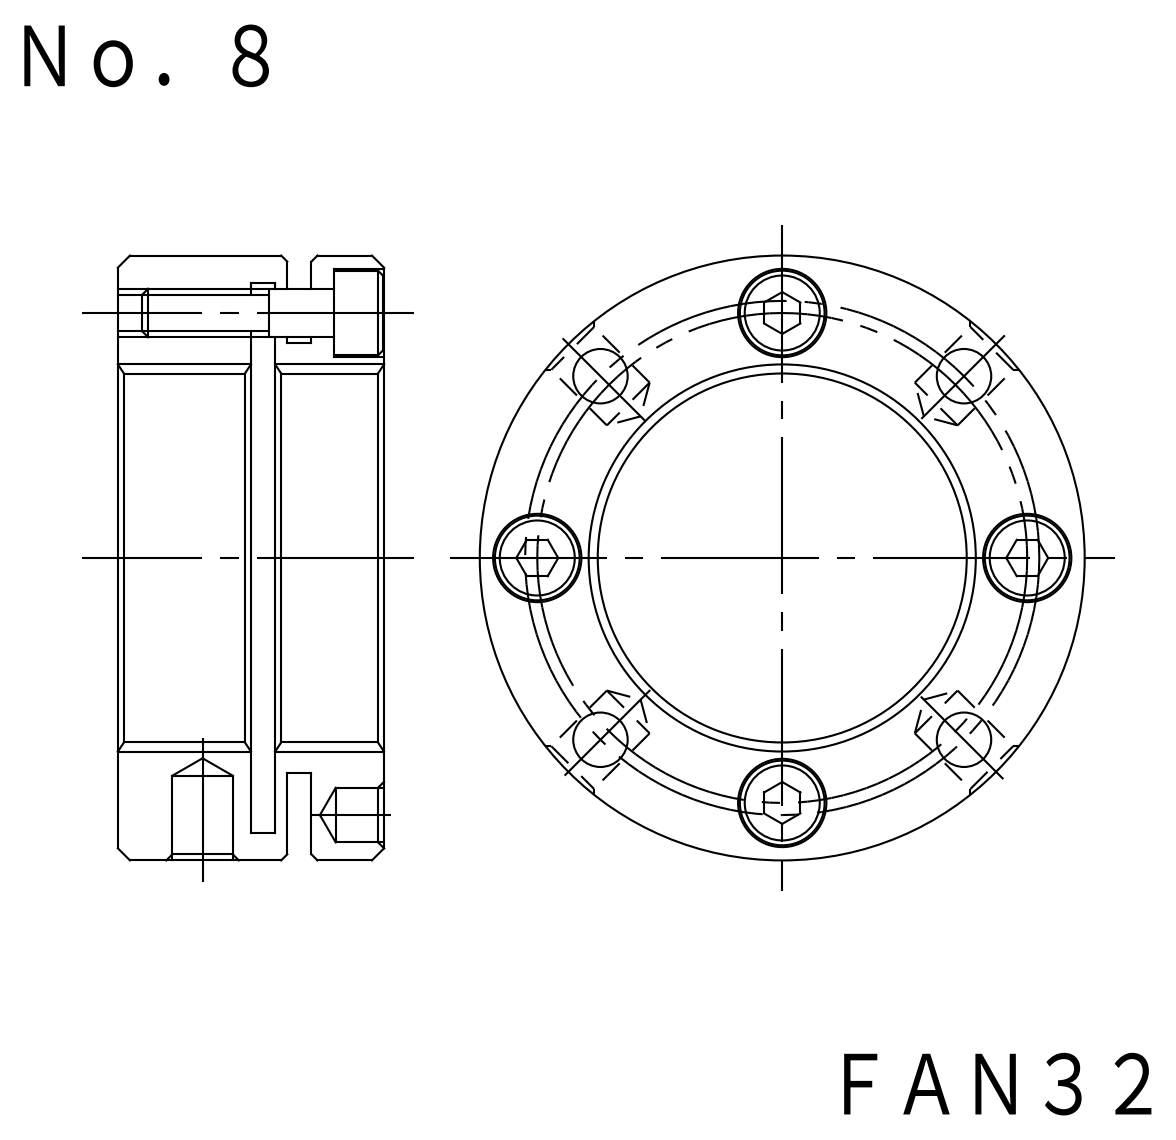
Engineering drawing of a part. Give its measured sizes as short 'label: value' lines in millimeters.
name: FKD FAN32; M4X16_default
written by: SolidWorks 2012 (CONFIG_CONTROL_DESIGN)
unit: mm
bodies: 5 solids, 142 faces (50 planar, 76 cylindrical, 16 other)
size: 50 × 50 × 22
volume: 21 255 mm³; area: 14 419 mm²
holes: 4× ⌀3.24, 4× ⌀4.3, 4× ⌀4.5, 4× ⌀7.3, 2× ⌀5, 1× ⌀32, 1× ⌀46
bosses: 4× ⌀7, 4× ⌀4, 1× ⌀50, 1× ⌀36
face distances: 2, 3, 11, 22, 16, 14, 8, 6, 5, 13
hole spacings: 15.99, 38.58, 20.5, 21.26, 28.99, 30.06, 41, 42.51
